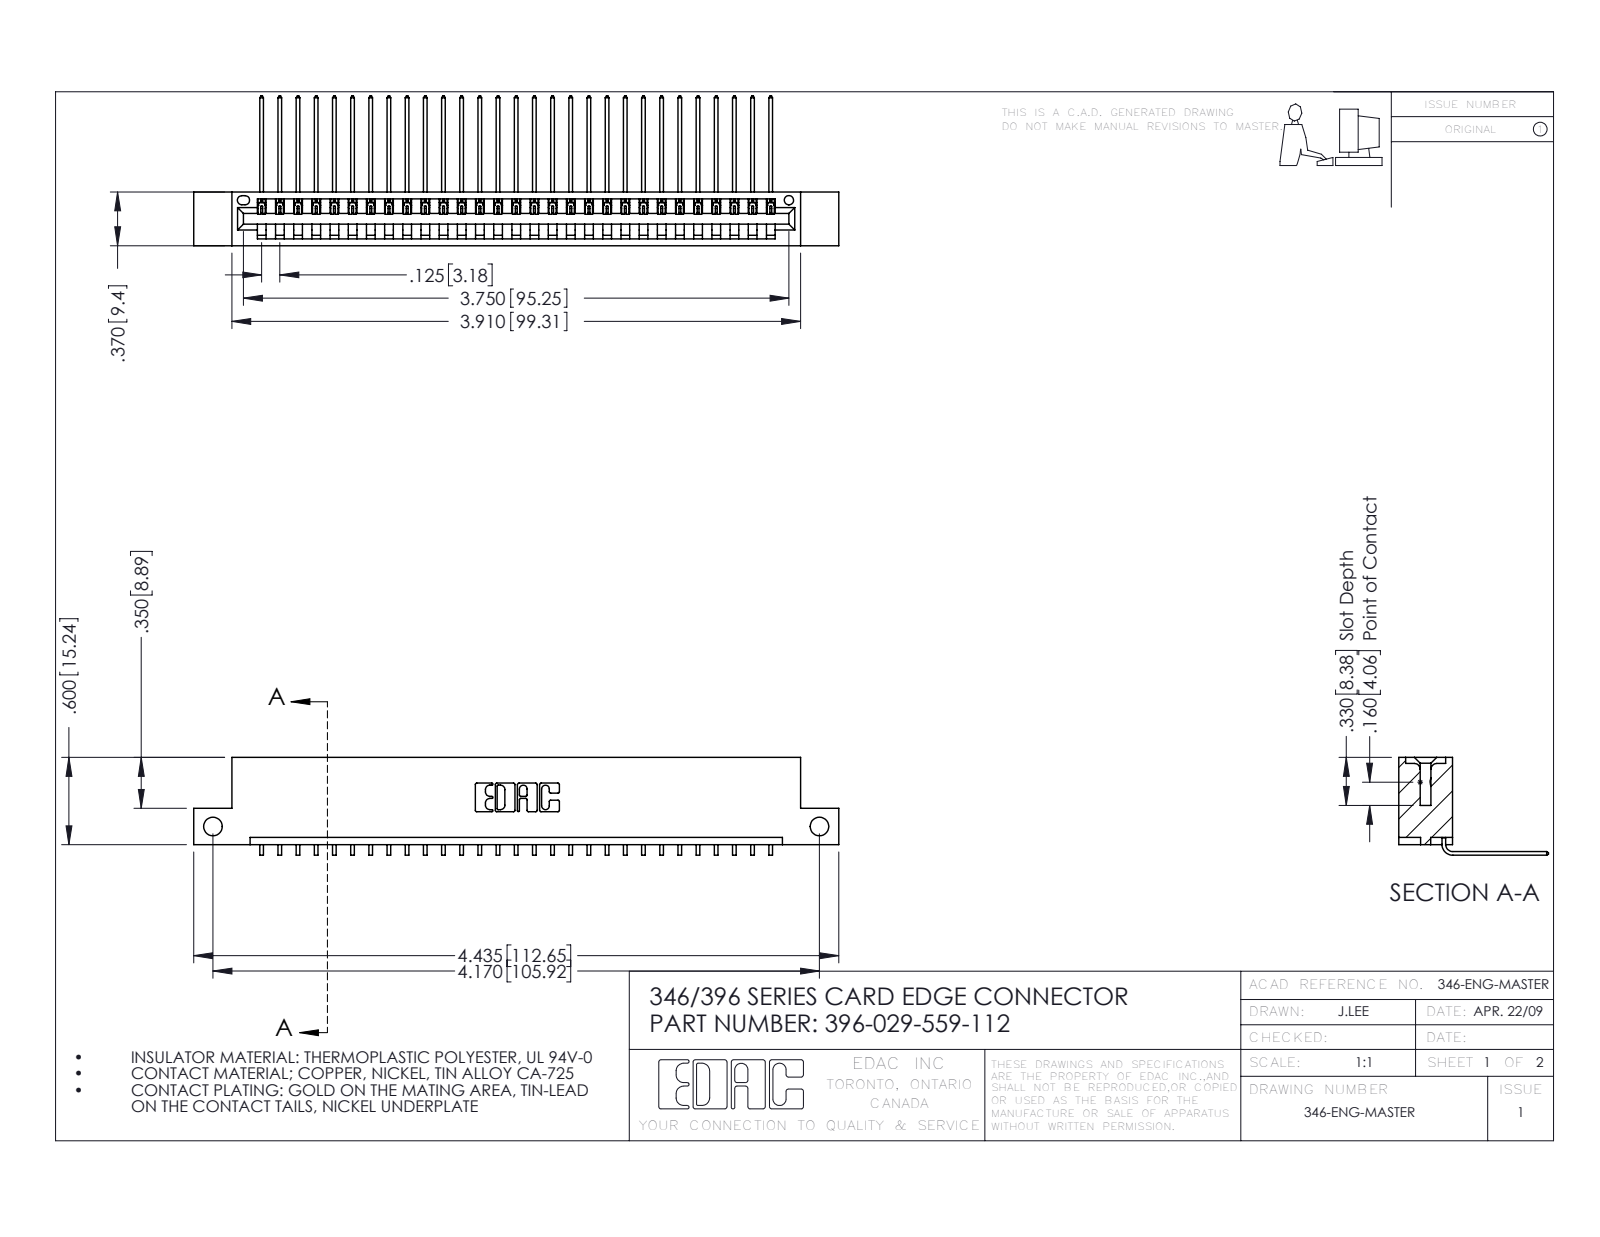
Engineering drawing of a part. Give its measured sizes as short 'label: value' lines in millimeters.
name: 345-292-001_558 559 Tail - 1; 396-029-559-112; 346 Part_Flush Mounting Lugs - Side Mount
written by: SolidWorks 2016 (CONFIG_CONTROL_DESIGN)
unit: mm
bodies: 30 solids, 1862 faces (1294 planar, 568 cylindrical, 0 other)
size: 112.6 × 26.2 × 17.1
volume: 10 700 mm³; area: 13 660 mm²
holes: 2× ⌀3.3, 1× ⌀1.6
rounds: 58× R0.2, 22× R0.3, 6× R0.2, 6× R0.8, 3× R0.7, 2× R0.8, 2× R1, 1× R0.4
face distances: 1.2, 8.2, 9.4, 6.4, 1.8, 0.6, 7.6, 3.8, 5.6, 2.5
hole spacings: 105.9
